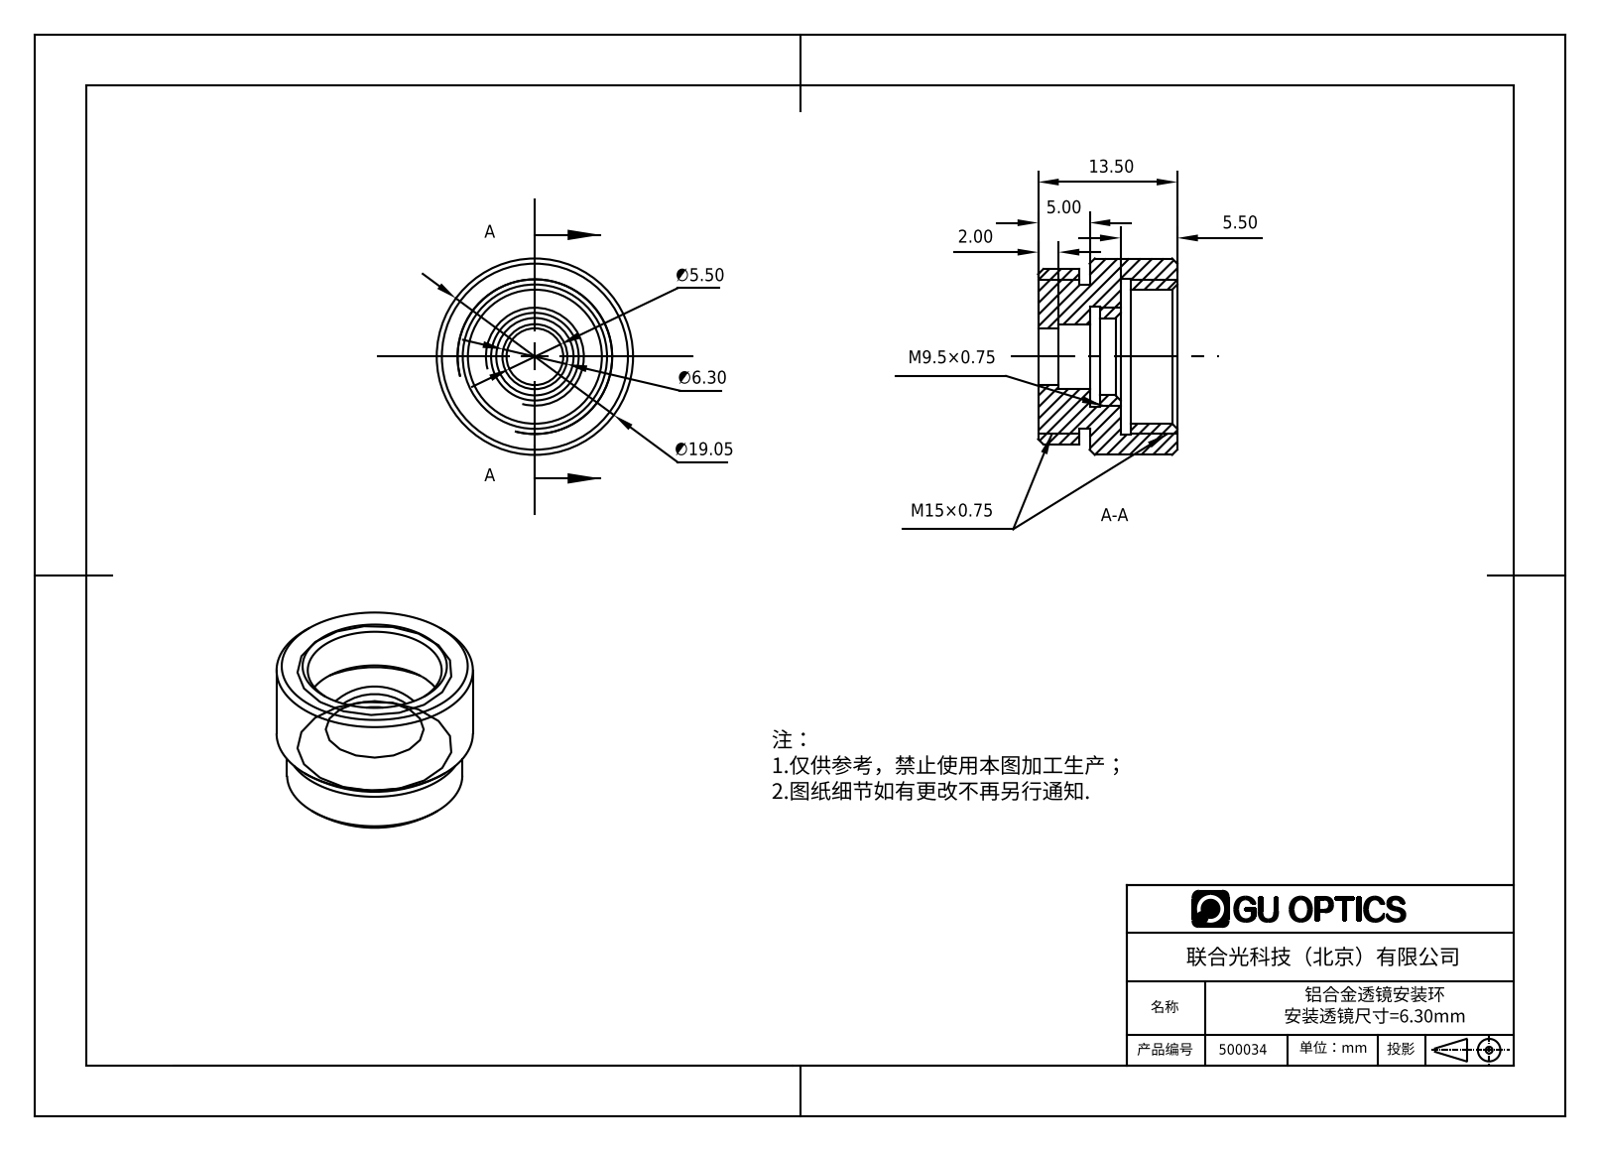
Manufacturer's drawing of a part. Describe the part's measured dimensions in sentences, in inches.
The part is named "500034". Its 3-D file was written by "SolidWorks 2016 (AUTOMOTIVE_DESIGN)". It is 1 solid with 37 faces: 9 planar, 18 cylindrical and 10 other. Overall it measures 0.75 by 0.75 by 0.531 inches. Its volume is 0.145 cubic inches and its surface area 2.984 square inches. Round holes: 1 of diameter 0.217, 1 of diameter 0.248, 1 of diameter 0.295, 1 of diameter 0.382, 1 of diameter 0.512, 1 of diameter 0.598. Round bosses or shafts: 1 of diameter 0.75, 1 of diameter 0.669, 1 of diameter 0.551. The main face-to-face distances are 0.157, 0.197, 0.118, 0.039, 0.315, 0.531, 0.335, 0.217, 0.079, 0.374.
